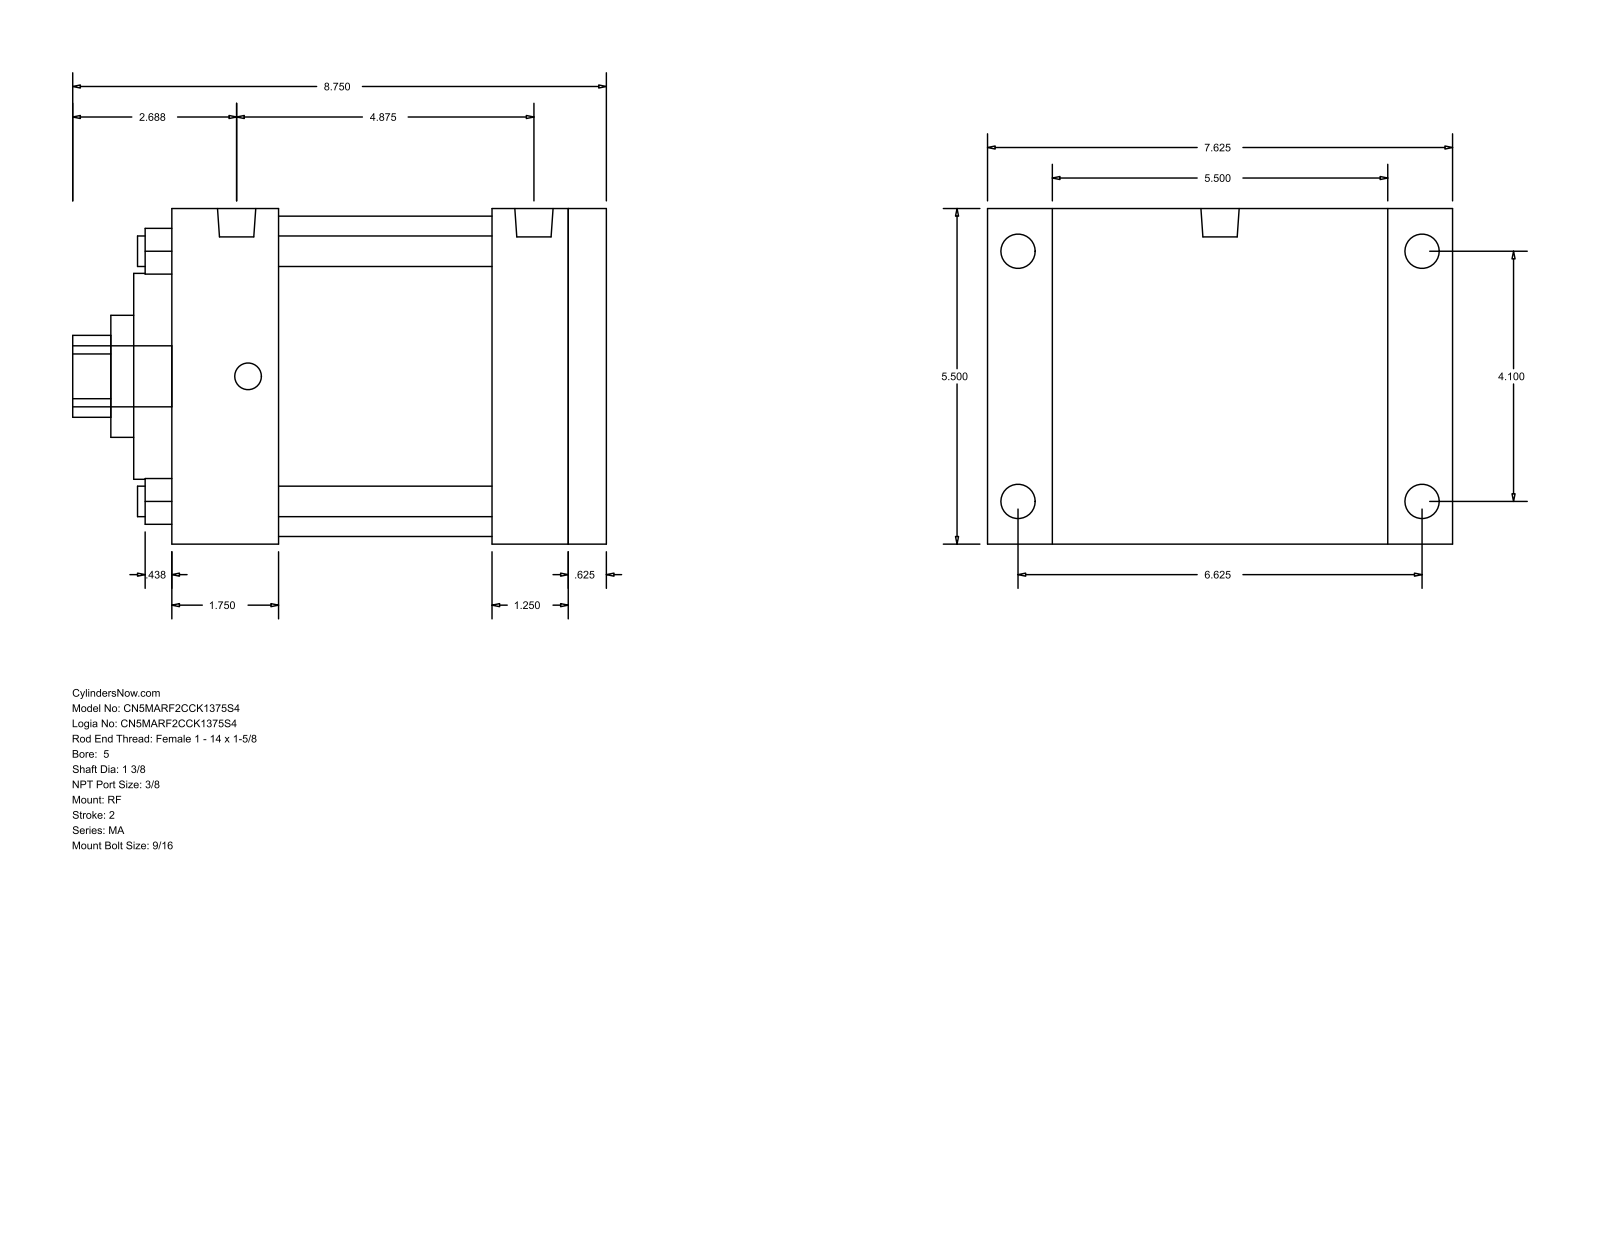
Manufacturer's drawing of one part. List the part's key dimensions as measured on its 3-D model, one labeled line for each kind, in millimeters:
Part name (STEP PRODUCT): MA_RF__0500_1.375
STEP written by: GSSL Pune (CONFIG_CONTROL_DESIGN)
Units: millimetres
Bodies: 0 solids, 94 faces (65 planar, 29 cylindrical, 0 other)
Overall size (bounding box): 222.25 × 193.68 × 139.7
Round holes (diameter × count): ⌀12.7 ×4, ⌀34.92 ×1, ⌀50.8 ×1, ⌀85.72 ×1, ⌀133.35 ×1
Round bosses / shafts (diameter × count): ⌀14.29 ×4, ⌀11.11 ×4, ⌀15.93 ×2, ⌀25.4 ×1
Partial cylindrical surfaces — rounded edges, fillets, slot ends (radius × count): R17.06 ×1
Main face-to-face distances: 139.7, 180.98, 15.87, 165.11, 44.45, 120.66, 136.53, 133.35, 88.9, 31.76
Hole centre spacings: 73.64, 104.14, 147.28
